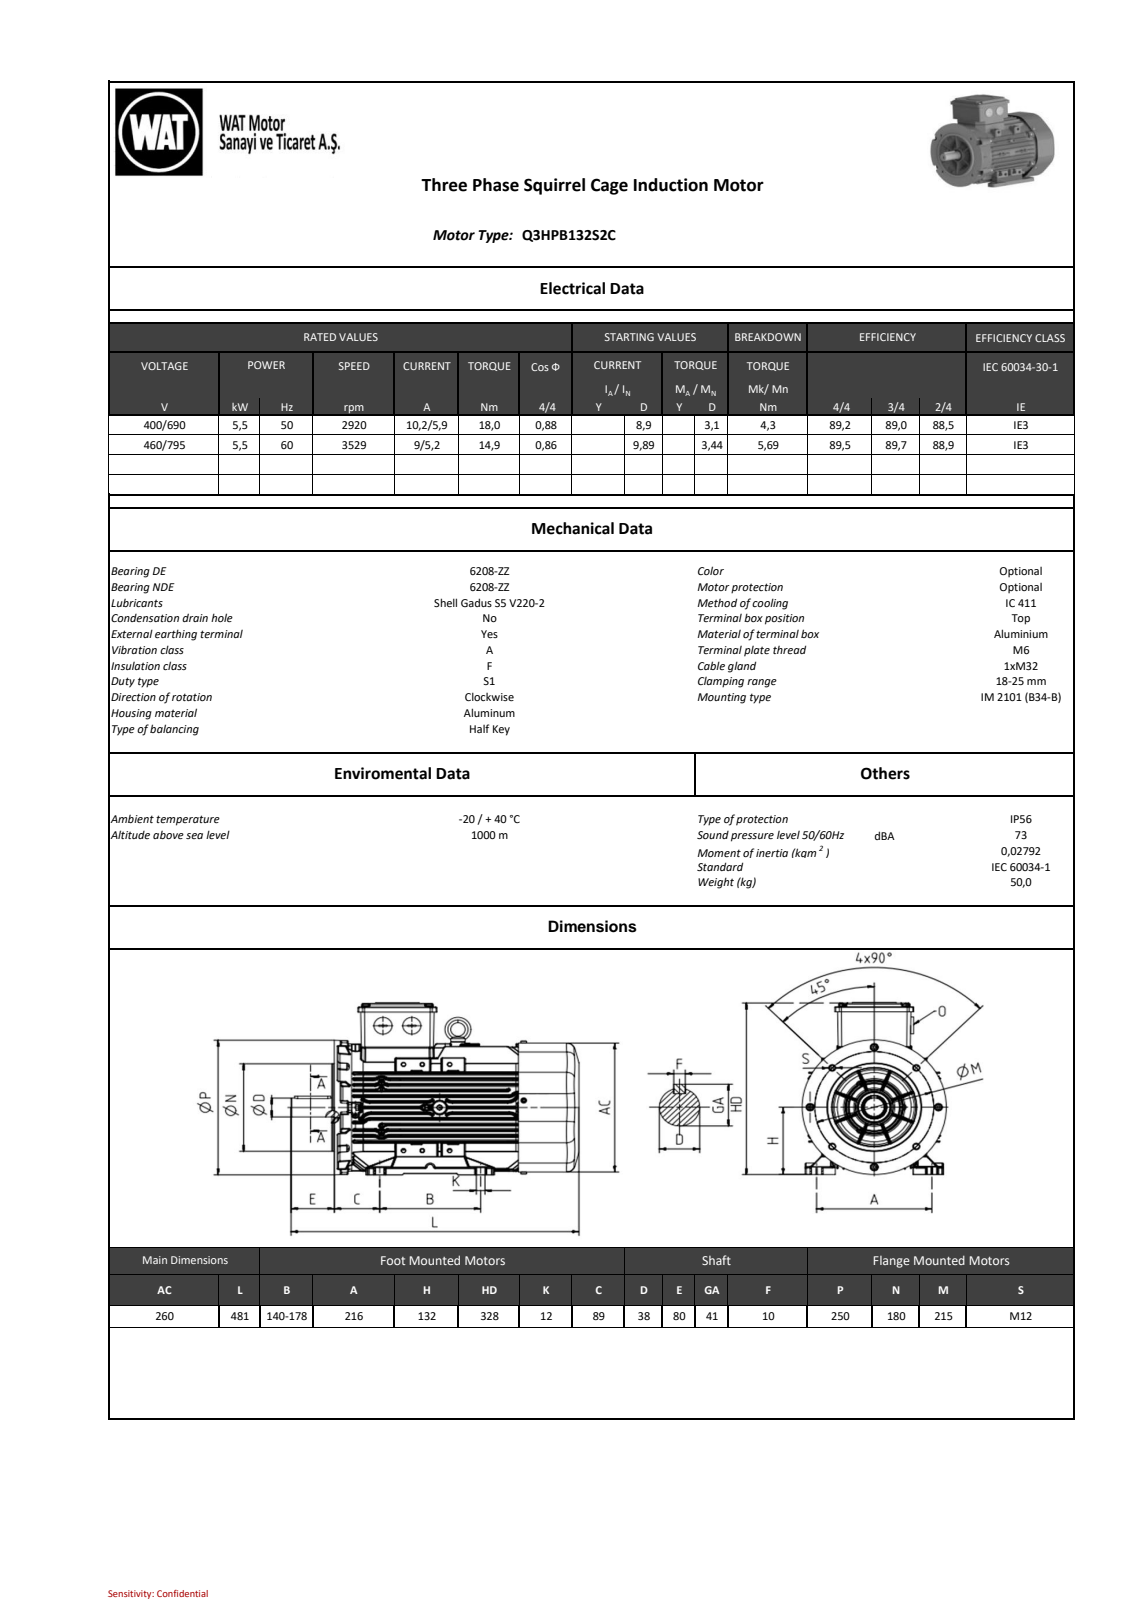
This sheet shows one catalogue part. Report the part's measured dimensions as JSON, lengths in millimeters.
{"part_name": "AA_objects", "step_written_by": "SIEMENS PLM Software NX2206.8101 (AP203_CONFIGURATION_CONTROLLED_3D_DESIGN_OF_MECHANICAL_PARTS_AND_ASSEMBLIES_MIM_LF)", "units": "millimeters", "bodies": {"solids": 0, "faces": 7671, "planar": 1835, "cylindrical": 2958, "other": 2878}, "overall_size": [480.49, 323.2, 260.12], "round_holes": [[5.5, 1], [14, 1], [24.4, 1], [82, 1], [180, 1]], "round_bosses_or_shafts": [[8, 10], [38, 3], [13, 2], [230.5, 1], [86.77, 1], [45, 1], [40, 1], [37.6, 1]], "partial_cylinders_radius": [[0.8, 880], [1, 645], [0.5, 61], [2, 38], [3, 33], [60, 16], [26, 12], [28, 12]], "face_to_face_distances": [10.42, 1.5, 10.56, 10.28, 20.84, 125.58, 94.46, 104.9, 115.18, 94.48], "hole_center_spacings": [74.95]}
